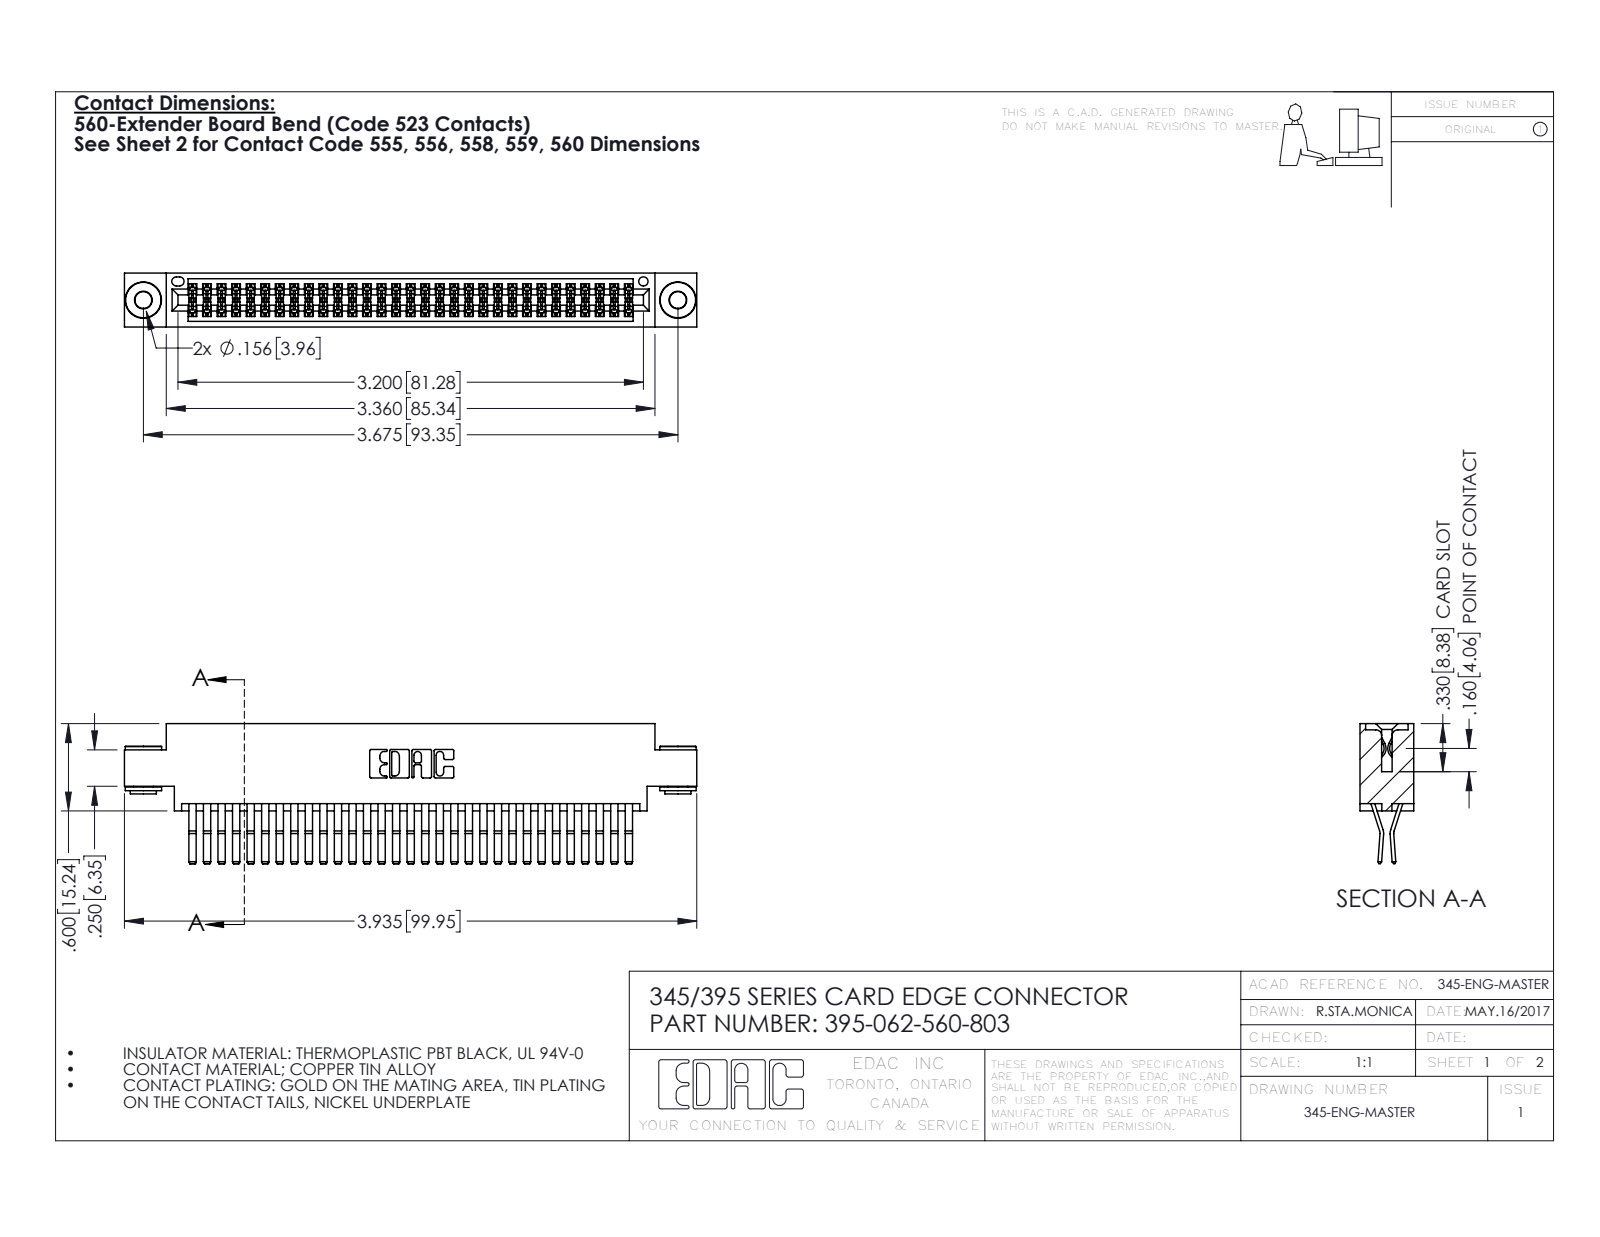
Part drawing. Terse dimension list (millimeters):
name: 345-250-002_345-250-002-102; 345-292-001_560 Tail; 395-062-560-803; 345 Part_0.170 Offset - 0.156 Dia-TH
written by: SolidWorks 2016 (CONFIG_CONTROL_DESIGN)
unit: mm
bodies: 65 solids, 3392 faces (2140 planar, 1244 cylindrical, 8 other)
size: 99.9 × 24.4 × 9.4
volume: 9 910 mm³; area: 15 850 mm²
holes: 2× ⌀2.9, 2× ⌀4, 1× ⌀1.6
bosses: 2× ⌀6.4, 2× ⌀4.6, 2× ⌀3.5
rounds: 94× R0.2, 22× R0.3, 6× R0.2, 6× R0.8, 3× R0.7, 2× R0.3, 2× R0.4, 2× R0.5
face distances: 0.6, 1.8, 7.6, 9.4, 5.1, 2.5, 6.9, 5.7, 4.4, 3.8
hole spacings: 6.9, 87.4, 93.3
